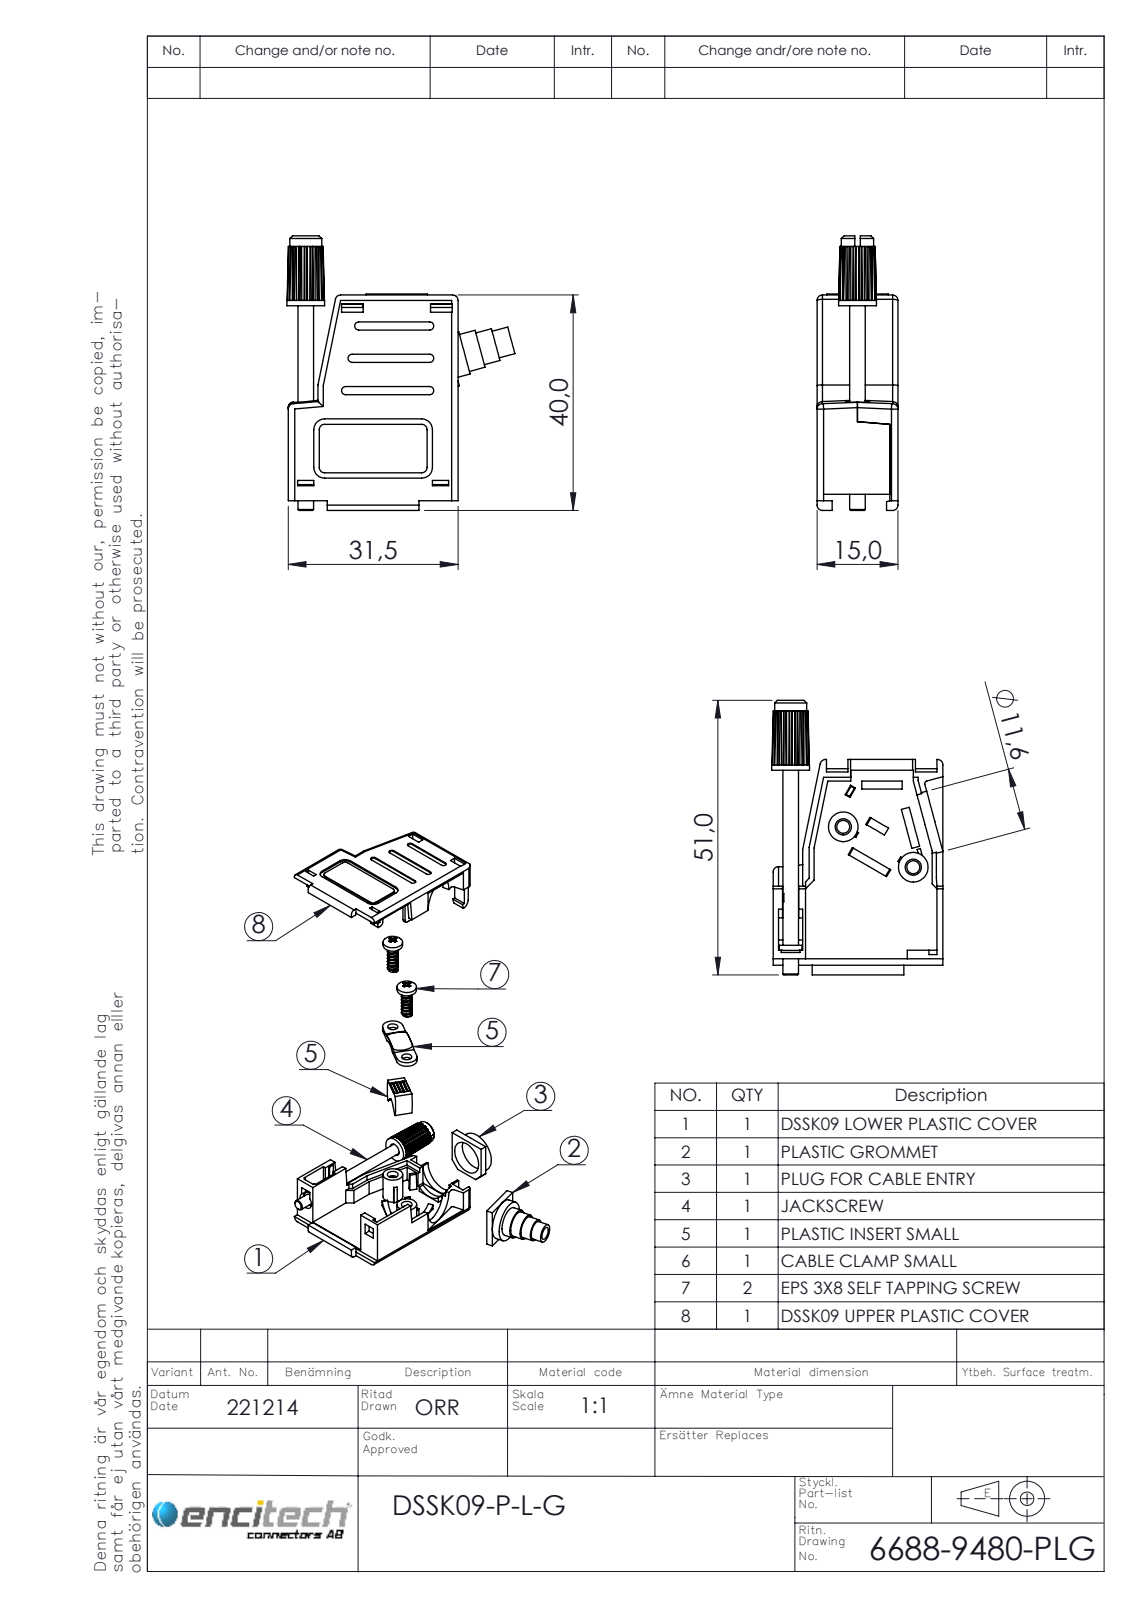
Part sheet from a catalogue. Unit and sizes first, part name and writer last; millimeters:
Units: millimetres
Overall size (bounding box): 51 × 42.29 × 15
Round holes (diameter × count): ⌀2.4 ×2, ⌀2.8 ×2, ⌀3 ×2, ⌀3.5 ×2, ⌀4.5 ×2, ⌀5.5 ×1, ⌀6.5 ×1, ⌀9.4 ×1, ⌀11.5 ×1, ⌀11.6 ×1
Round bosses / shafts (diameter × count): ⌀5.5 ×2, ⌀5.45 ×2, ⌀2.46 ×2, ⌀11.4 ×1, ⌀11.3 ×1, ⌀8.1 ×1, ⌀7.1 ×1, ⌀7 ×1
Partial cylindrical surfaces — rounded edges, fillets, slot ends (radius × count): R1 ×20, R0.5 ×6, R0.75 ×6, R2 ×6, R1.2 ×4, R0.1 ×2, R1.5 ×2, R2.85 ×2
Main face-to-face distances: 13.3, 1.7, 1.5, 11.6, 15, 13.1, 1.2, 2, 1.6, 14.8
Hole centre spacings: 7.5, 15, 16.89
Volume: 7 748 mm³ · Surface area: 11 707 mm²
Bodies: 11 solids, 795 faces (545 planar, 184 cylindrical, 66 other)
Part name (STEP PRODUCT): 6822-0121-06 part 2; 6688-9480-PLG; 6811-0141-11 Part 2; 6830-0106-01 (+5 more)
STEP written by: SolidWorks 2021 (AUTOMOTIVE_DESIGN)
